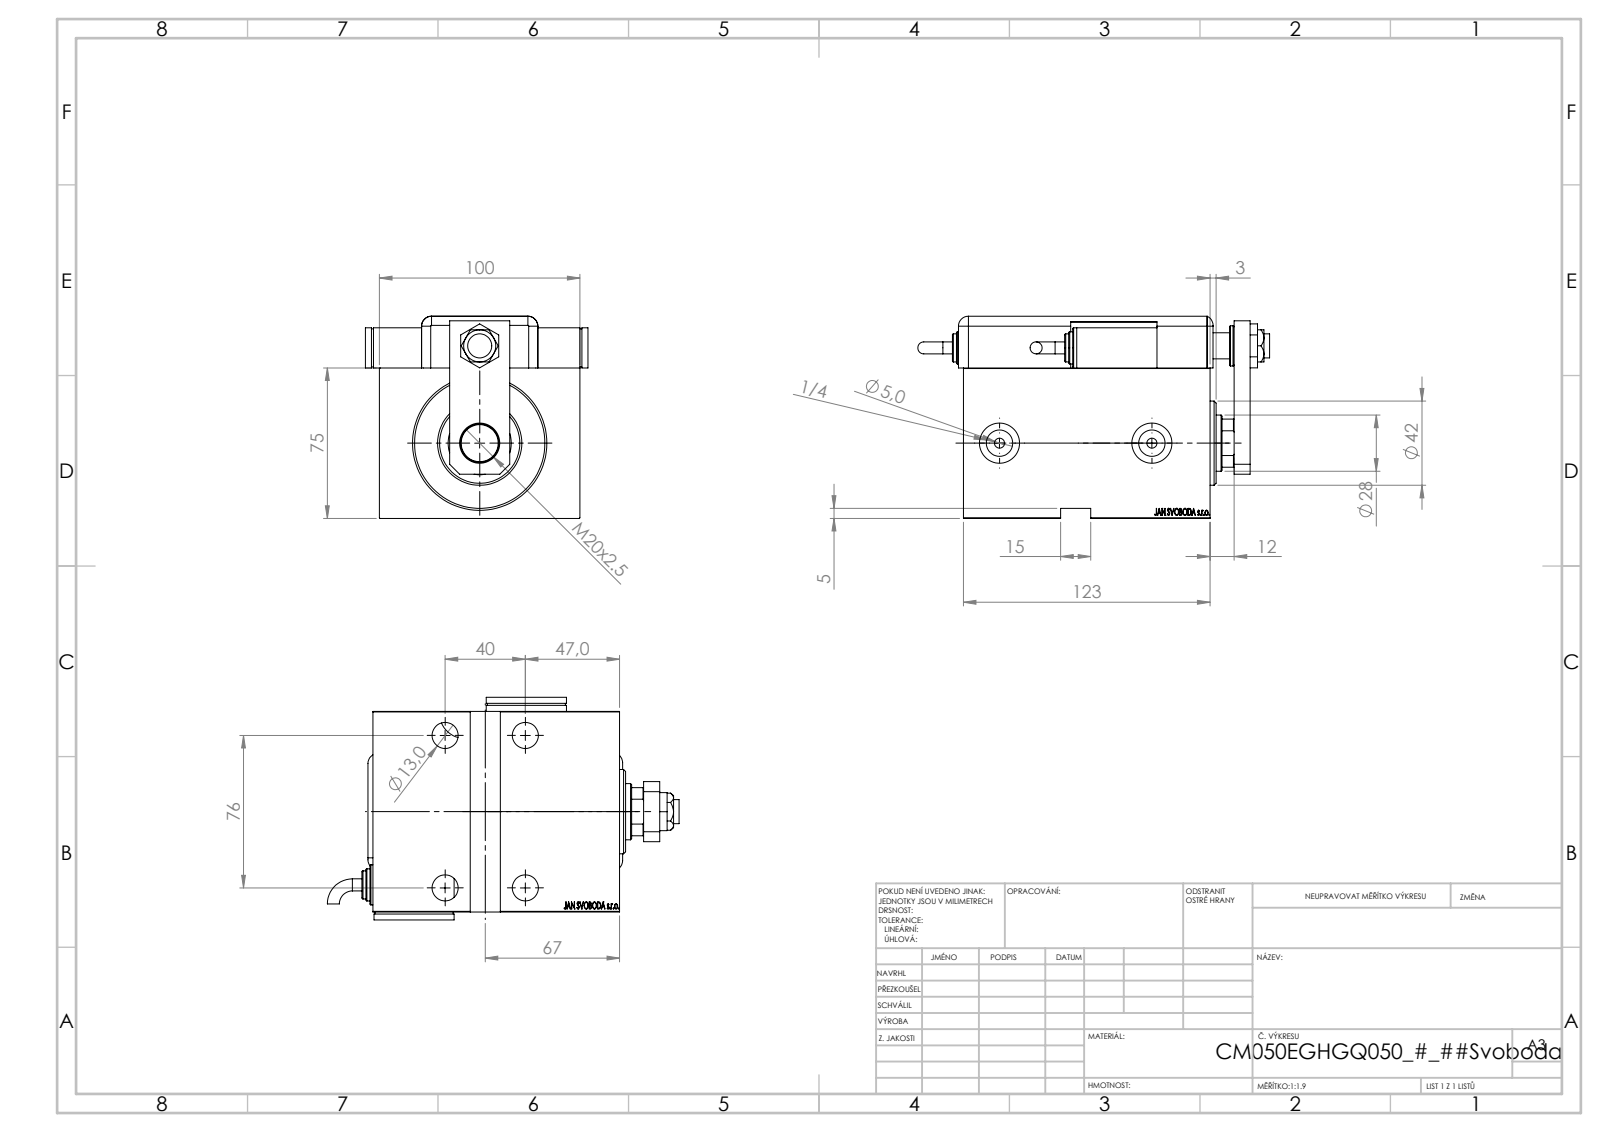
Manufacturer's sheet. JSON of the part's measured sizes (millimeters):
{"part_name": "SWITCH DIM A_G; SWITCH_Q_FRONT_BACK; NUT_D19; NUT_D13 (+7 more)", "step_written_by": "SolidWorks 2019 (CONFIG_CONTROL_DESIGN)", "units": "millimeters", "bodies": {"solids": 13, "faces": 1240, "planar": 616, "cylindrical": 107, "other": 517}, "overall_size": [175.46, 111, 100.8], "volume_mm3": 953166, "surface_area_mm2": 180527, "round_holes": [[13, 5], [19, 4], [20, 3], [4, 2], [5, 2], [8, 2], [13.16, 2], [12, 1], [14, 1], [18.5, 1], [28, 1], [31.5, 1]], "round_bosses_or_shafts": [[20, 3], [16, 2], [14, 2], [6, 2], [52, 1], [42, 1]], "partial_cylinders_radius": [[5, 9], [10, 1], [13.5, 1]], "face_to_face_distances": [3, 75, 100, 123, 100.8, 25.8, 14, 20, 109, 2.8], "hole_center_spacings": [76, 40, 47.2, 61.22, 82.87, 85.88, 91.59, 20]}
